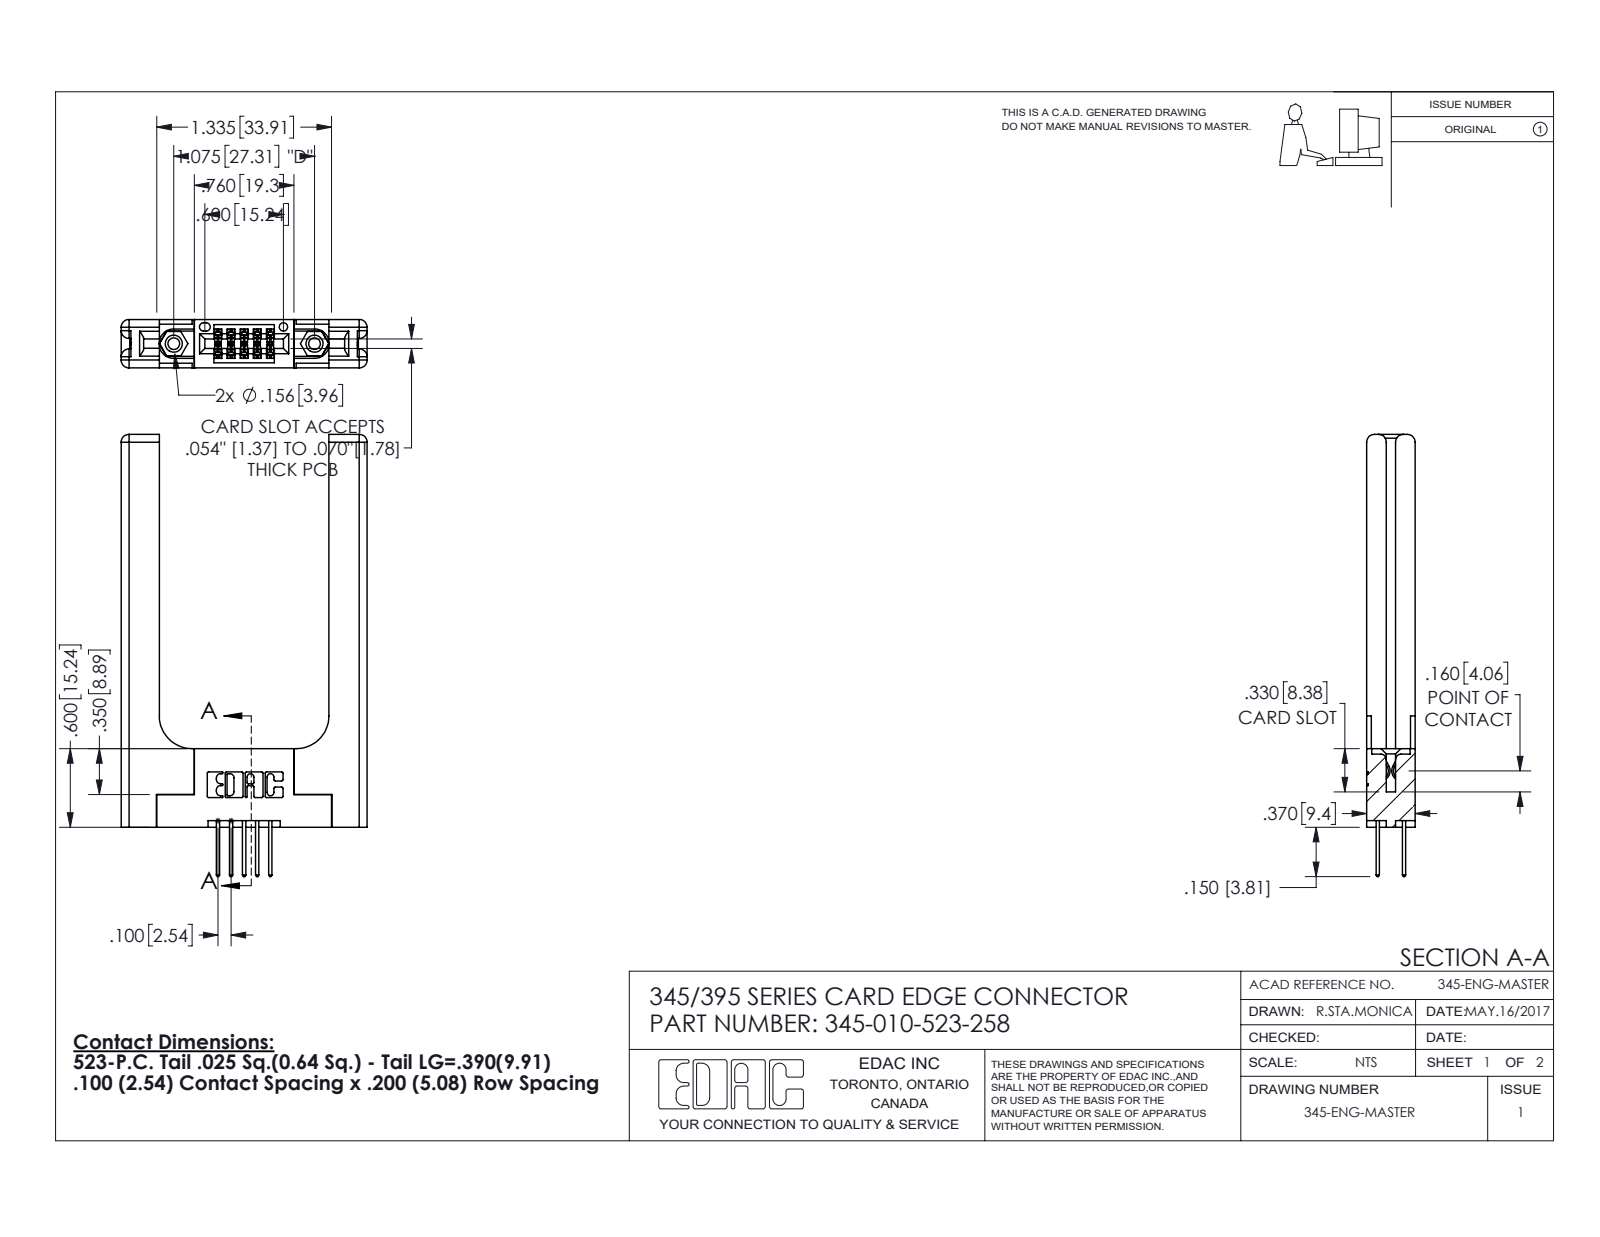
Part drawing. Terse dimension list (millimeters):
name: 345-292-001_345-293-123; 345-250-001_345-250-001-102; 345-220-058_345-220-058; 345 Part_Flush Mounting Lugs - 0.156 Dia-TH (+1 more)
written by: SolidWorks 2016 (CONFIG_CONTROL_DESIGN)
unit: mm
bodies: 15 solids, 882 faces (558 planar, 264 cylindrical, 60 other)
size: 85.8 × 47.7 × 9.4
volume: 12 800 mm³; area: 10 810 mm²
holes: 2× ⌀2.3, 2× ⌀3.2, 2× ⌀4, 1× ⌀1.6
bosses: 2× ⌀3.9
rounds: 22× R0.3, 16× R1.5, 15× R0.2, 10× R0.3, 6× R0.2, 6× R0.8, 3× R0.7, 2× R0.4
face distances: 9.4, 3.8, 5.6, 1.8, 2, 3.8, 32.9, 7.6, 5.1, 1.8
hole spacings: 6.9, 21.5, 27.3
